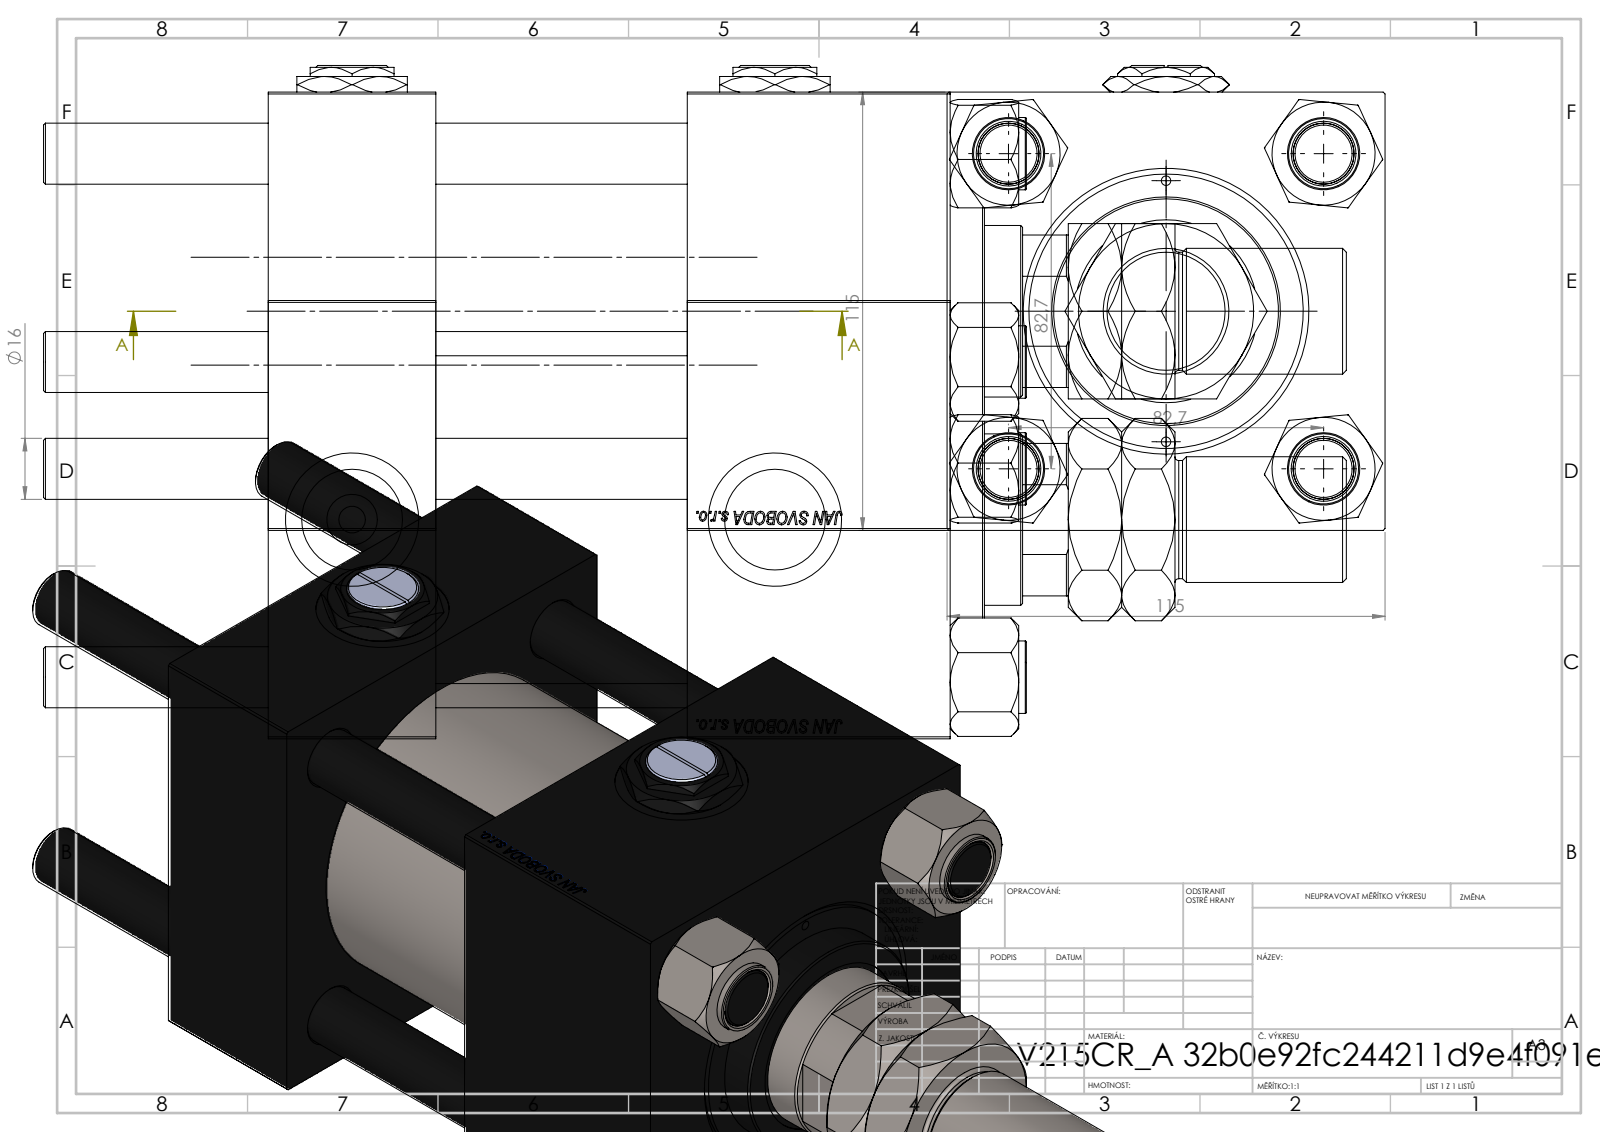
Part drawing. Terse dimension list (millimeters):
name: NUT_M5; MTA; V215CR_VCP; V215_VC_A (+3 more)
written by: SolidWorks 2019 (CONFIG_CONTROL_DESIGN)
unit: mm
bodies: 14 solids, 1336 faces (632 planar, 96 cylindrical, 608 other)
size: 342 × 122 × 115
volume: 1 973 000 mm³; area: 319 693 mm²
holes: 4× ⌀16, 2× ⌀2.5, 2× ⌀7, 2× ⌀26.44, 2× ⌀35, 1× ⌀31.5, 1× ⌀45, 1× ⌀48, 1× ⌀61, 1× ⌀72, 1× ⌀80
bosses: 4× ⌀19, 1× ⌀86, 1× ⌀60, 1× ⌀33, 1× ⌀31
rounds: 1× R22
face distances: 115, 44, 179, 135, 110, 69, 66, 46, 20, 89
hole spacings: 41.96, 58.48, 82.7, 86.17, 34.25, 116.96, 68.5, 111
